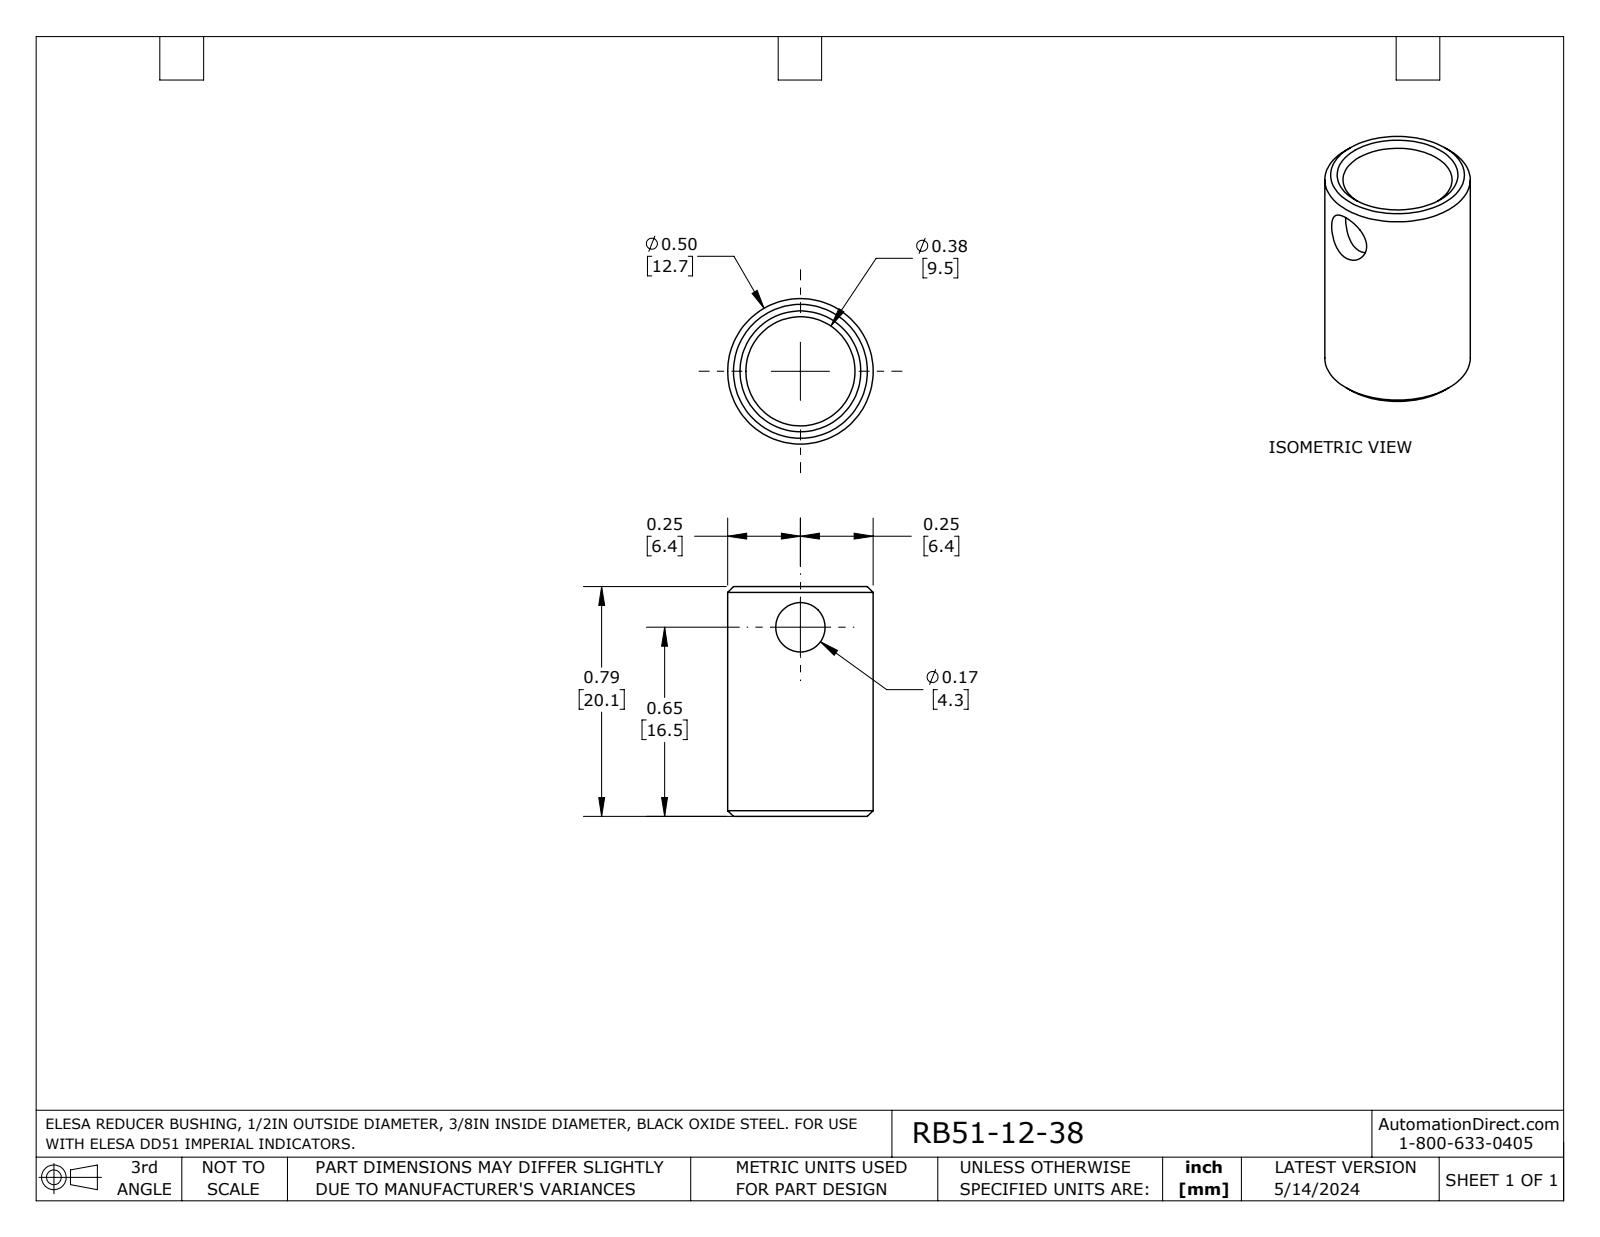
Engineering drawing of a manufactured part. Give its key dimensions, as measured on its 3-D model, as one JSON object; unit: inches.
{"part_name": "RB51 1_2-3_8", "step_written_by": "SolidWorks 2023 (AUTOMOTIVE_DESIGN)", "units": "inches", "bodies": {"solids": 1, "faces": 9, "planar": 2, "cylindrical": 3, "other": 4}, "overall_size": [0.79, 0.5, 0.5], "volume_in3": 0.065, "surface_area_in2": 2.267, "round_holes": [[0.17, 1], [0.375, 1]], "round_bosses_or_shafts": [[0.5, 1]], "face_to_face_distances": [0.79]}
